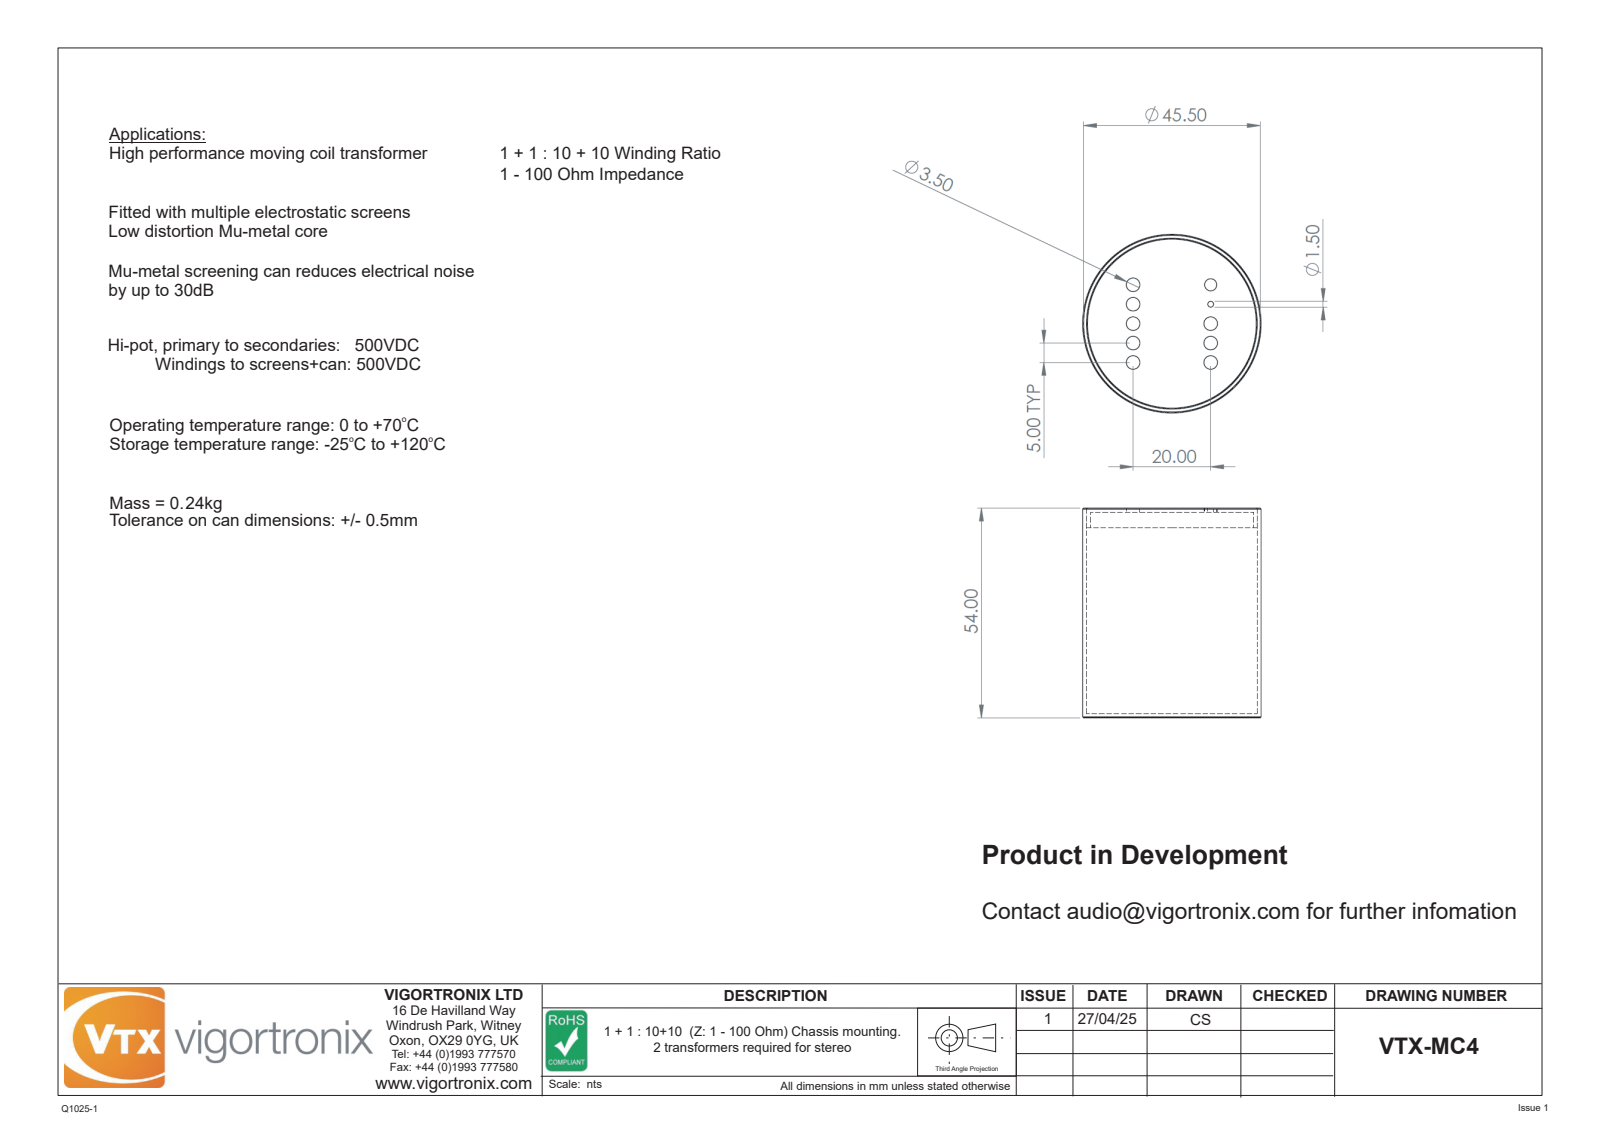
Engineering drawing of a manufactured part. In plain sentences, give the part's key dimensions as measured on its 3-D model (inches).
The part is named "CLID047; VTX-MC4; VTX-MC4 Bobbin; CAN046". Its 3-D file was written by "SolidWorks 2024 (AUTOMOTIVE_DESIGN)". It is 3 solids with 70 faces: 20 planar, 44 cylindrical and 6 other. Overall it measures 2.323 by 1.811 by 1.811 inches. Its volume is 1.052 cubic inches and its surface area 38.66 square inches. Round holes: 9 of diameter 0.138, 1 of diameter 0.059, 1 of diameter 1.654, 1 of diameter 1.732. Round bosses or shafts: 8 of diameter 0.039, 1 of diameter 1.811. The main face-to-face distances are 2.087, 0.039, 2.126, 2.047, 0.197, 1.929, 1.89, 0.157, 0.394, 1.535. The hole center spacings are 0.197, 0.394, 0.812, 0.787, 0.88, 0.44, 0.557, 0.591.
